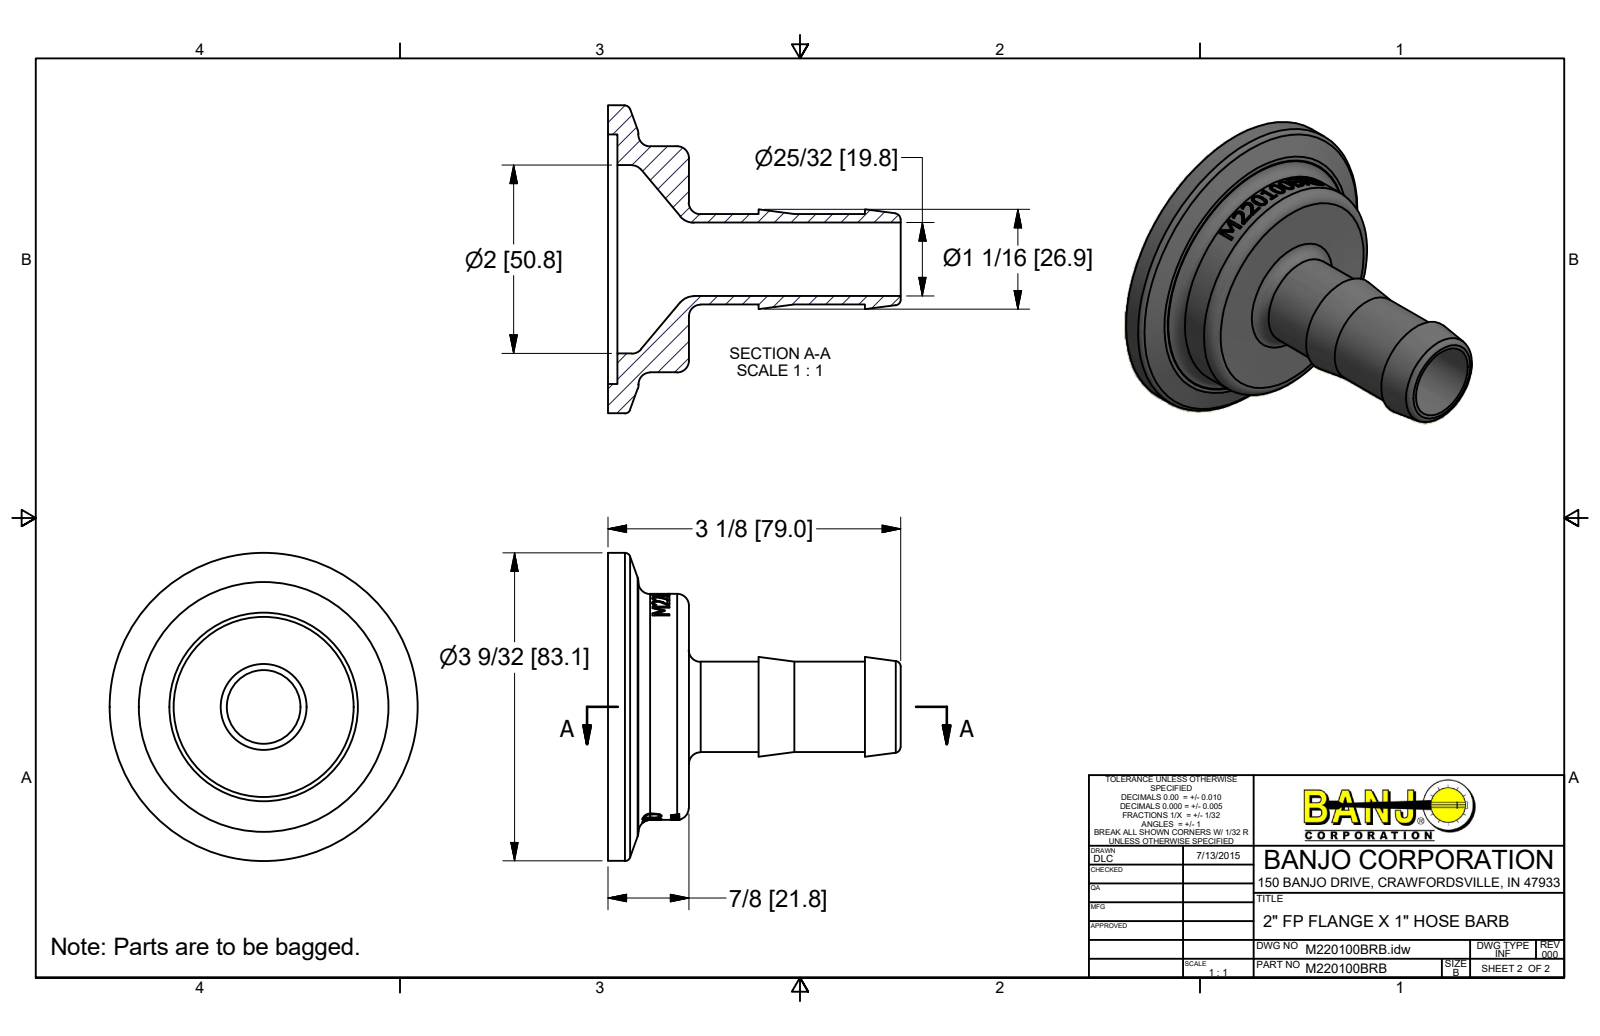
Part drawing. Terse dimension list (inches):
name: M220100BRB; M220100BRBU
written by: Autodesk Inventor 2018 (AUTOMOTIVE_DESIGN)
unit: in
bodies: 1 solid, 448 faces (196 planar, 54 cylindrical, 198 other)
size: 3.27 × 3.27 × 3.11
volume: 3.559 in³; area: 37.53 in²
holes: 1× ⌀0.78, 1× ⌀2, 1× ⌀2.65
bosses: 1× ⌀3.27, 1× ⌀2.4, 1× ⌀0.96
rounds: 1× R1.17
face distances: 0.86, 0.1, 0.76, 1.6, 2.73, 1.5, 2.63, 0.74, 1.87, 1.13
